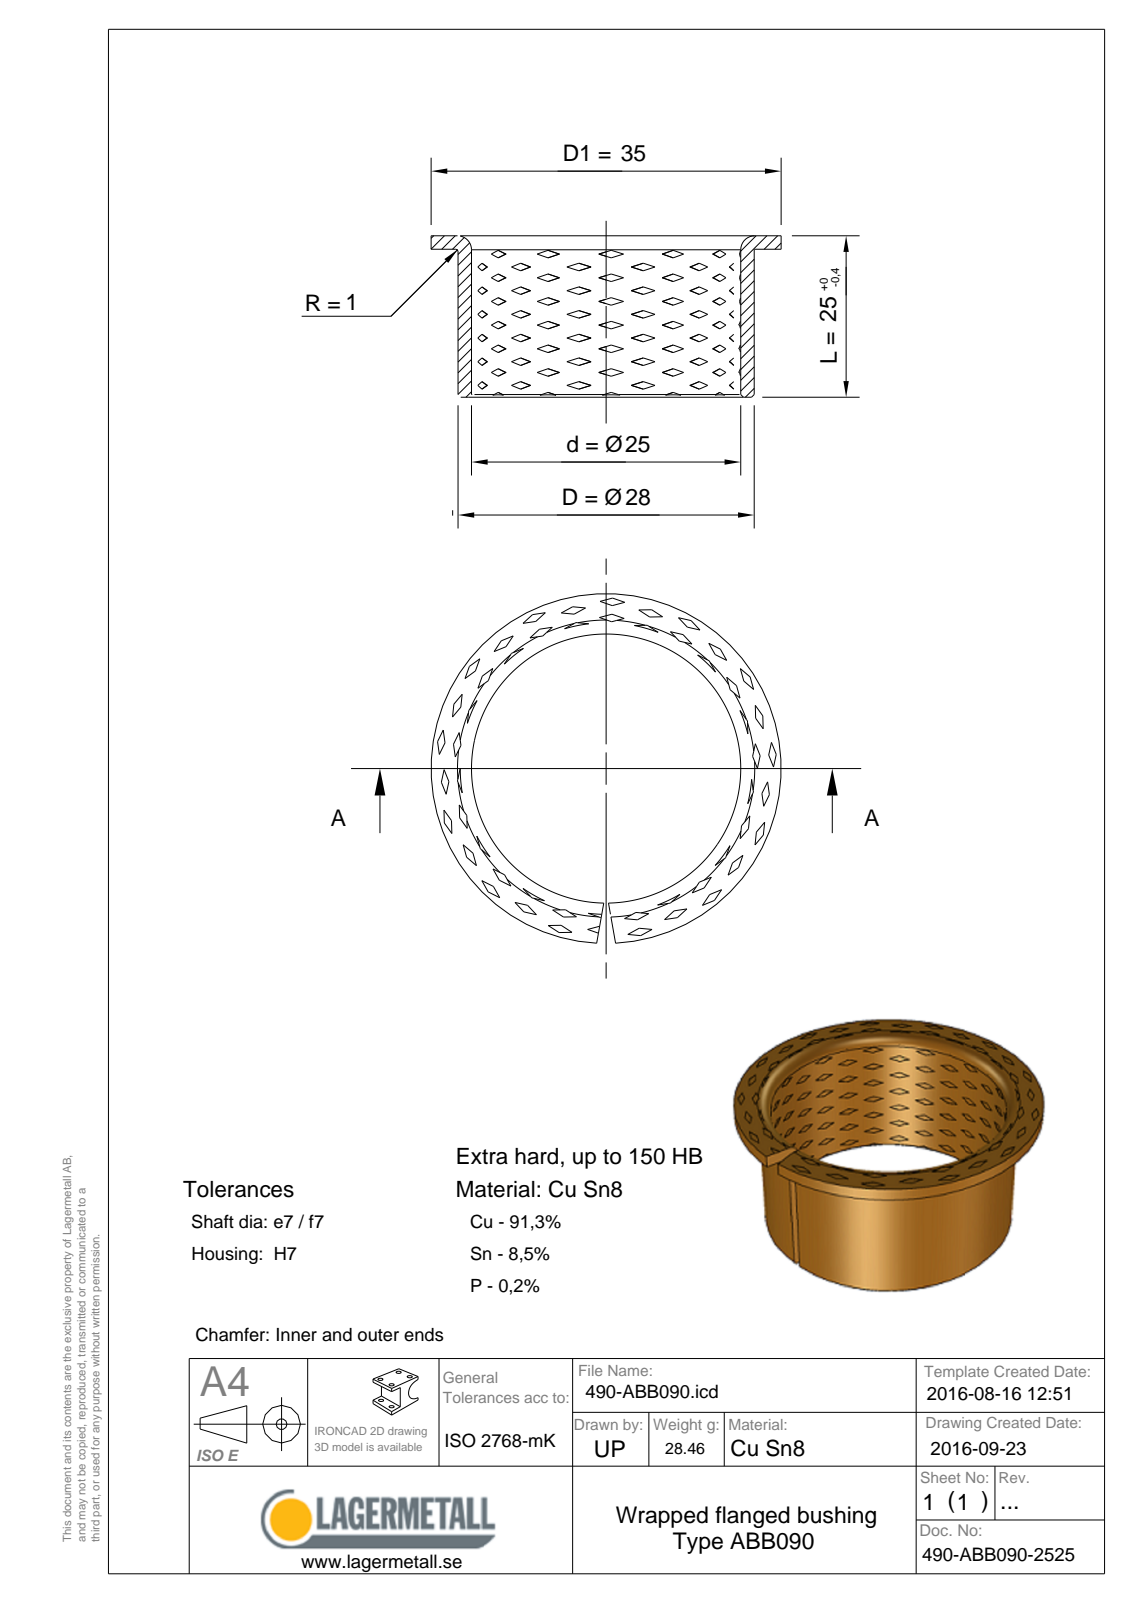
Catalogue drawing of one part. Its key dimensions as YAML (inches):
step_written_by: "Spatial InterOp 3D (CONFIG_CONTROL_DESIGN)"
units: inches
bodies: {solids: 1, faces: 25, planar: 5, cylindrical: 8, other: 12}
overall_size: [1.378, 1.378, 0.984]
volume: 0.214
surface_area: 7.798
round_holes:
  - {diameter: 0.984, count: 1}
round_bosses_or_shafts:
  - {diameter: 1.378, count: 1}
  - {diameter: 1.102, count: 1}
face_to_face_distances: [0.059, 0.925, 0.984]
